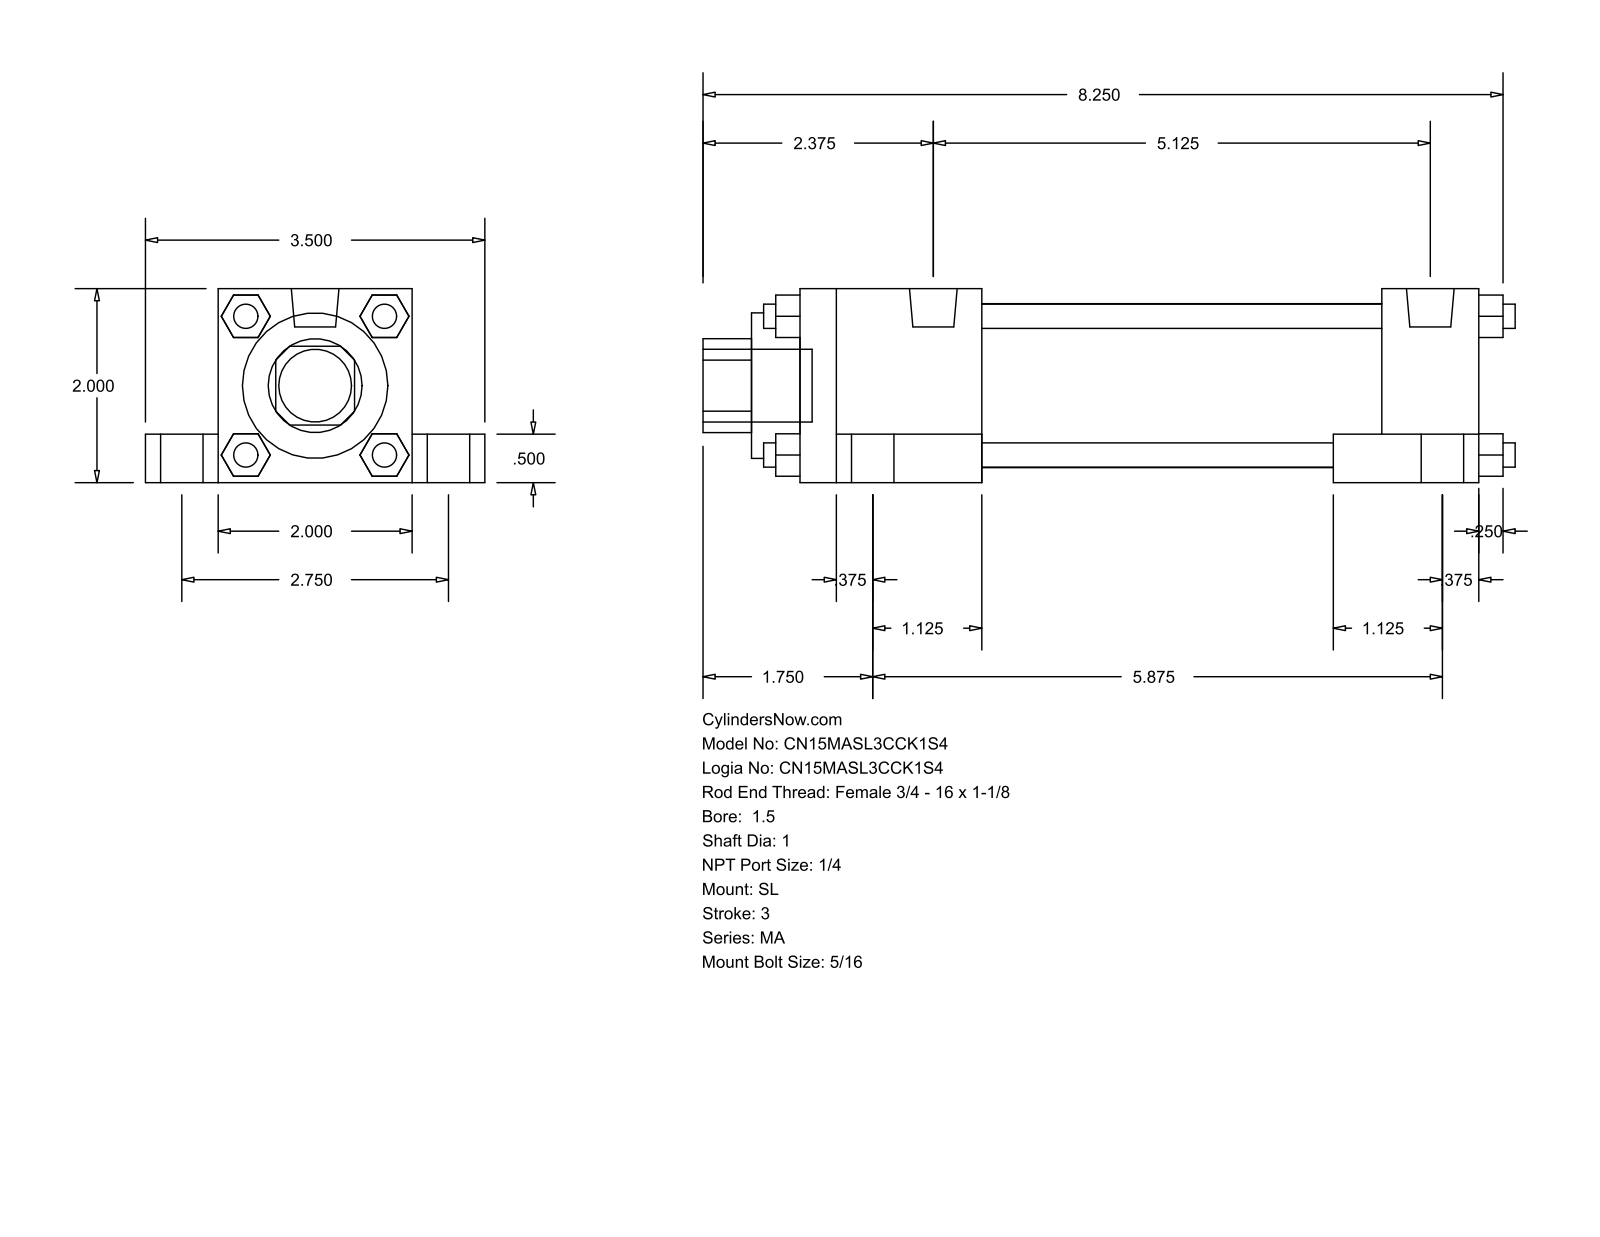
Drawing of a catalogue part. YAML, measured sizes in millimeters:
part_name: "MA_SL__0150_1"
step_written_by: "GSSL Pune (CONFIG_CONTROL_DESIGN)"
units: millimeters
bodies: {solids: 0, faces: 148, planar: 112, cylindrical: 36, other: 0}
overall_size: [212.72, 88.9, 50.8]
round_holes:
  - {diameter: 25.4, count: 1}
  - {diameter: 38.1, count: 1}
  - {diameter: 42.93, count: 1}
round_bosses_or_shafts:
  - {diameter: 17.46, count: 4}
  - {diameter: 11.11, count: 4}
  - {diameter: 7.94, count: 4}
  - {diameter: 6.35, count: 4}
  - {diameter: 12.49, count: 2}
  - {diameter: 19.05, count: 1}
partial_cylinders:
  - {radius: 12.29, count: 1}
face_to_face_distances: [50.8, 12.7, 19.05, 9.52, 69.85, 38.1, 6.35, 177.8, 25.4, 152.4]
